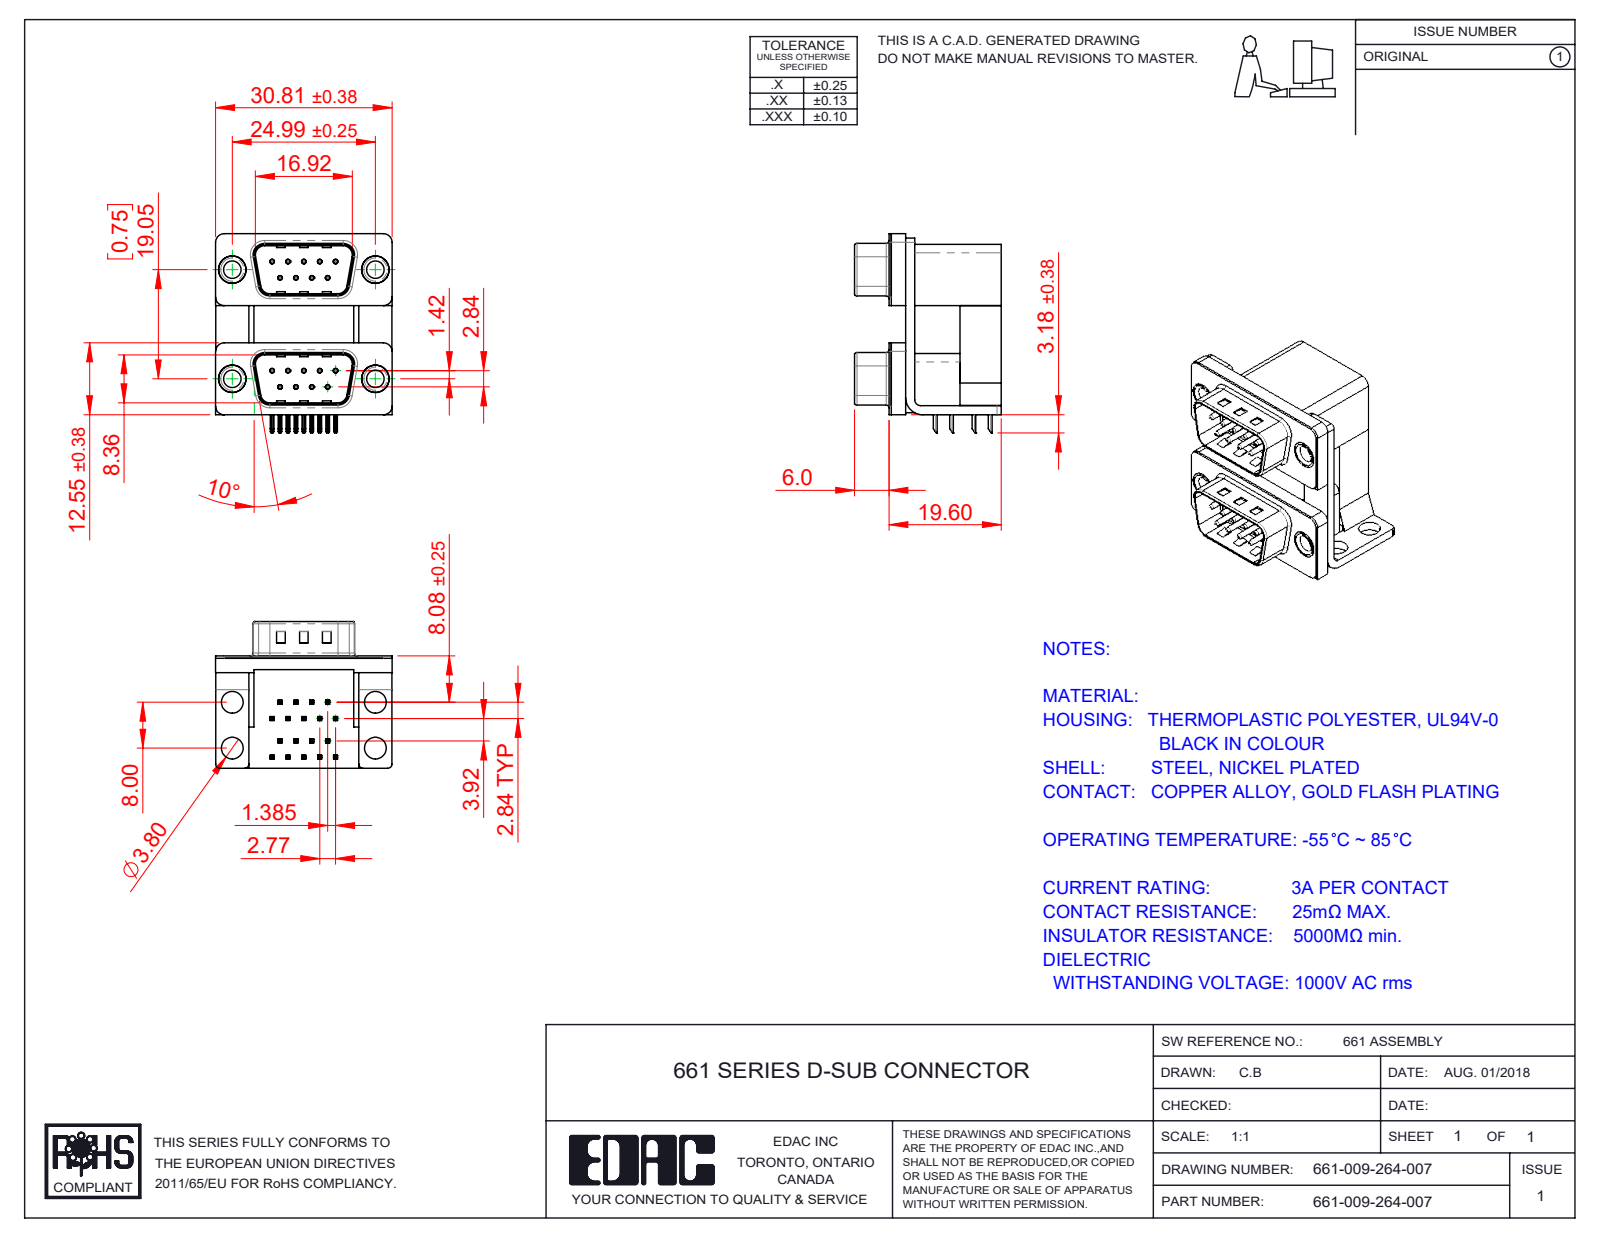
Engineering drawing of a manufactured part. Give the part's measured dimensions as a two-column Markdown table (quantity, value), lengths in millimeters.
| quantity | value |
| --- | --- |
| part name | 661 Contact Bottom Upper_M; 661 Housing Lower_09 Contacts; 661-009-264-007; 661 Contact Top Lower (+7 more) |
| STEP written by | SolidWorks 2020 (CONFIG_CONTROL_DESIGN) |
| units | millimeters |
| bodies | 29 solids, 1864 faces (1152 planar, 558 cylindrical, 154 other) |
| overall size | 34.78 × 30.81 × 25.6 |
| volume | 10 241 mm³ |
| surface area | 11 731 mm² |
| round holes (diameter × count) | 0.35 × 18, 0.8 × 18, 3.05 × 4, 3.5 × 4, 3.8 × 4, 4 × 4, 4.8 × 4, 5 × 4 |
| round bosses / shafts (diameter × count) | 0.75 × 18, 4.9 × 4, 4.75 × 4, 3.85 × 4 |
| partial cylindrical surfaces (radius × count) | 0.25 × 72, 0.12 × 36, 0.5 × 16, 1.5 × 14, 0.75 × 8, 0.9 × 8, 1.6 × 8, 2 × 8 |
| main face-to-face distances | 0.4, 2.5, 19.05, 16.7, 19.2, 7.2, 10.69, 9.5, 12, 1.6 |
| hole center spacings | 3.16, 2.77, 19.25, 19.05, 5.54, 19.84, 16.27, 21.93 |
